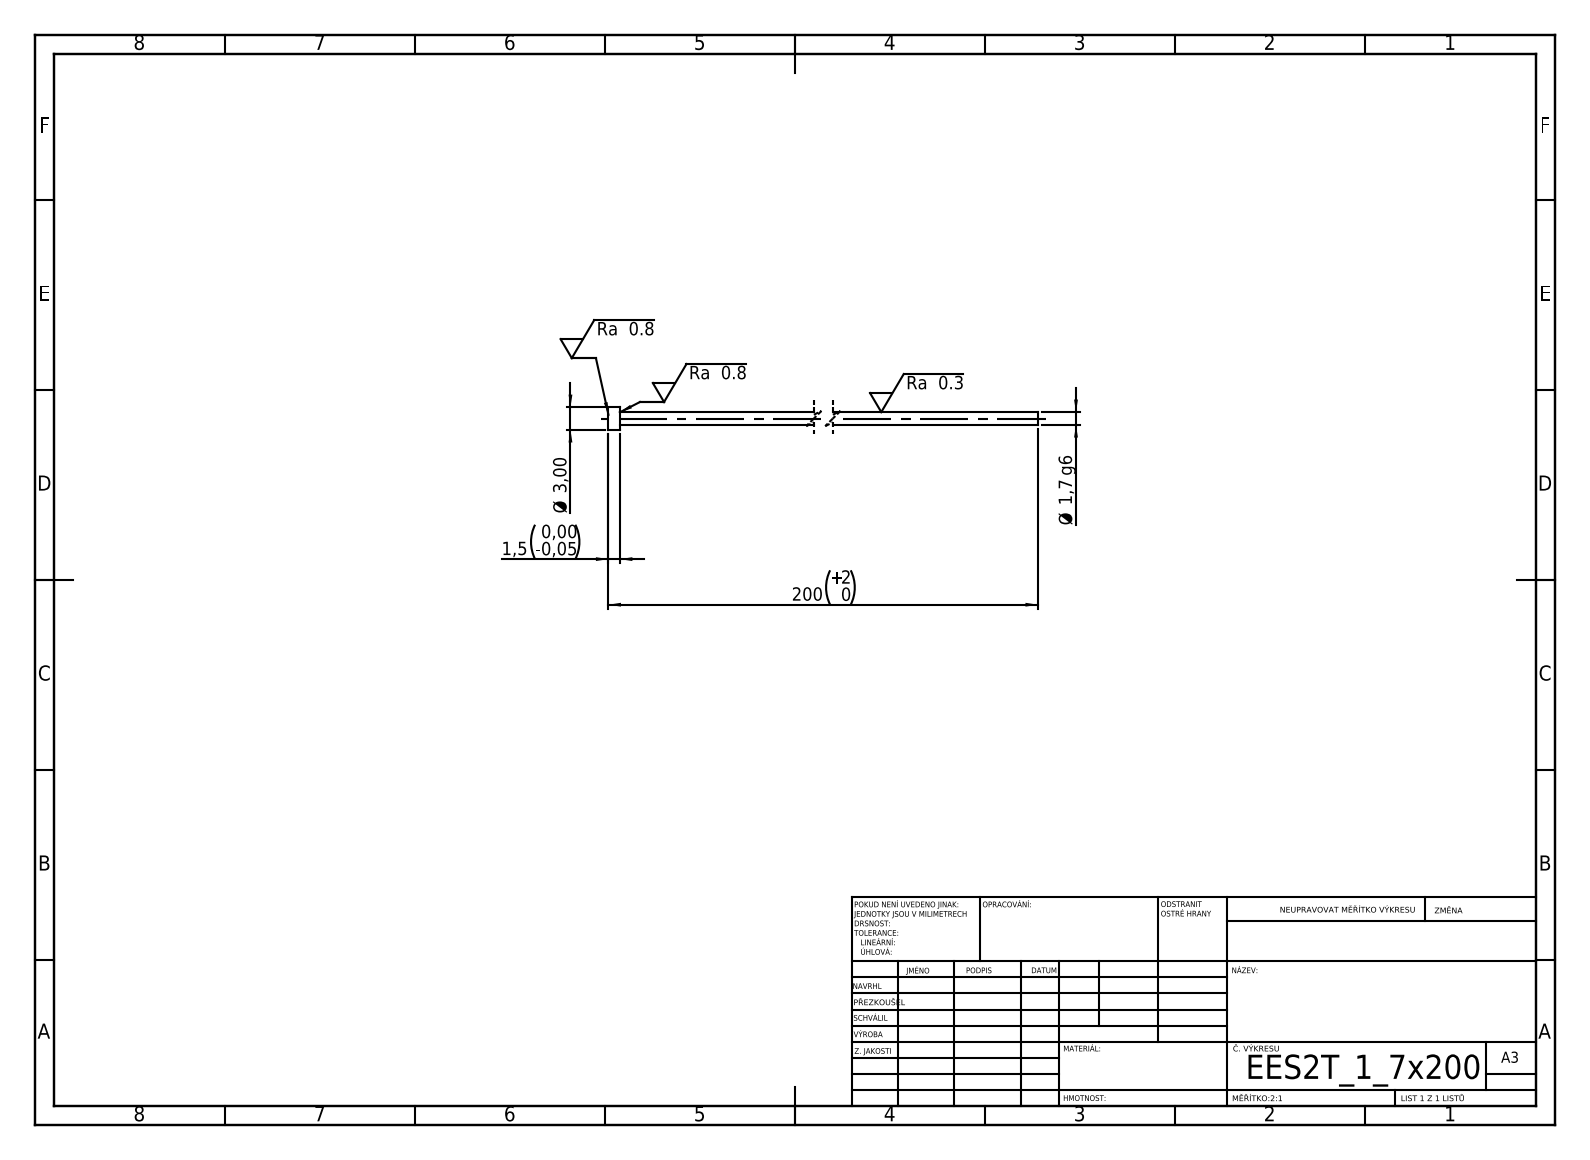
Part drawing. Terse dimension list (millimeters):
written by: SolidWorks 2019 (CONFIG_CONTROL_DESIGN)
unit: mm
bodies: 1 solid, 7 faces (3 planar, 4 cylindrical, 0 other)
size: 200 × 3 × 3
volume: 461 mm³; area: 1 088 mm²
bosses: 1× ⌀3, 1× ⌀1.7
face distances: 1.5, 200, 198.5
